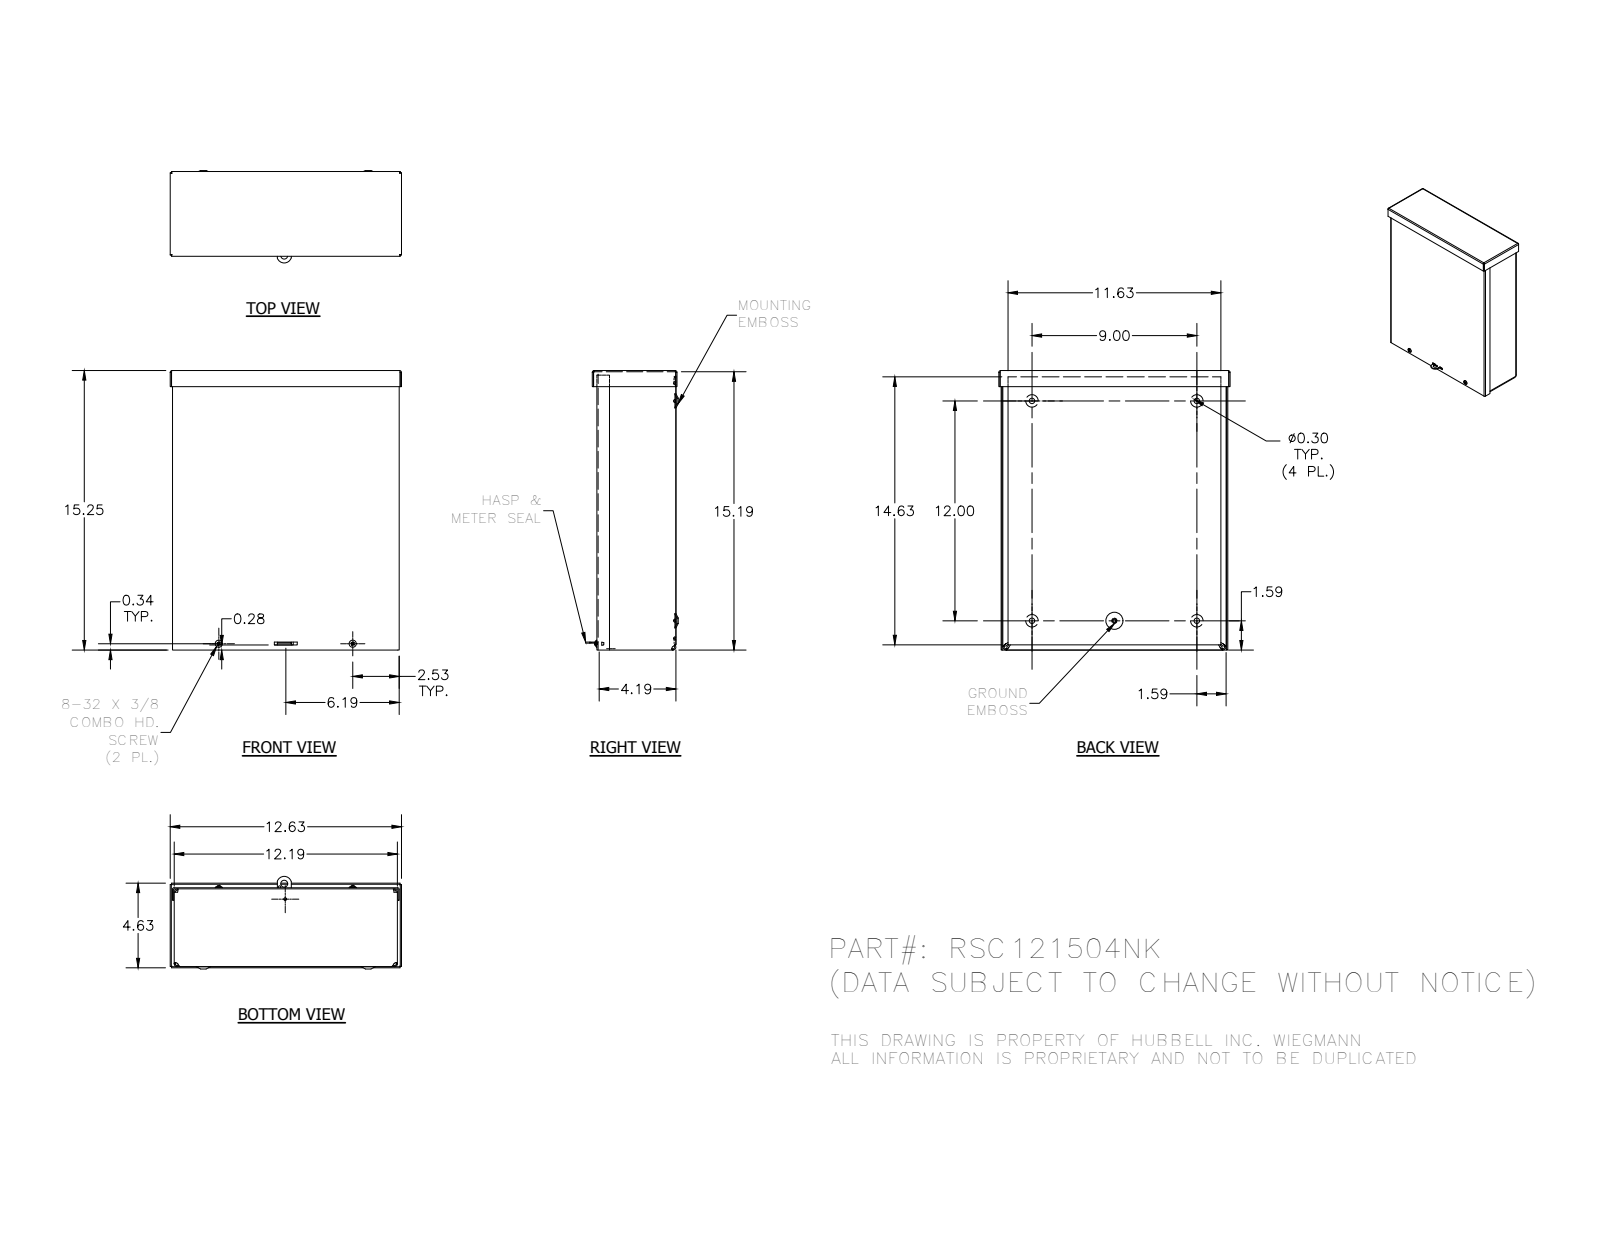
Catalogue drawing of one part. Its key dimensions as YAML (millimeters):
part_name: "RSC121504NK_WRAP; RSC1215NK_LID; RSC1204NK_CAP; 3183 (+3 more)"
step_written_by: "Autodesk Inventor 2014 (AUTOMOTIVE_DESIGN)"
units: millimeters
bodies: {solids: 7, faces: 377, planar: 163, cylindrical: 78, other: 136}
overall_size: [387.36, 320.68, 130.17]
volume: 776103
surface_area: 996300
round_holes:
  - {diameter: 7.62, count: 4}
  - {diameter: 7.95, count: 4}
  - {diameter: 3.76, count: 2}
  - {diameter: 3.17, count: 1}
  - {diameter: 3.45, count: 1}
  - {diameter: 3.96, count: 1}
  - {diameter: 4.19, count: 1}
  - {diameter: 9.52, count: 1}
round_bosses_or_shafts:
  - {diameter: 9.75, count: 2}
  - {diameter: 4.17, count: 2}
  - {diameter: 5.8, count: 1}
partial_cylinders:
  - {radius: 0.79, count: 8}
  - {radius: 2.37, count: 8}
  - {radius: 3.17, count: 8}
  - {radius: 4.75, count: 8}
  - {radius: 1.4, count: 4}
  - {radius: 1.57, count: 4}
  - {radius: 2.38, count: 4}
  - {radius: 2.97, count: 4}
face_to_face_distances: [1.58, 107.93, 106.35, 1.59, 109.52, 107.94, 1.57, 307.99, 384.19, 3.15]
hole_center_spacings: [34.43, 114.3, 185.75, 228.6, 304.8, 325.52, 332.44, 337.26]
